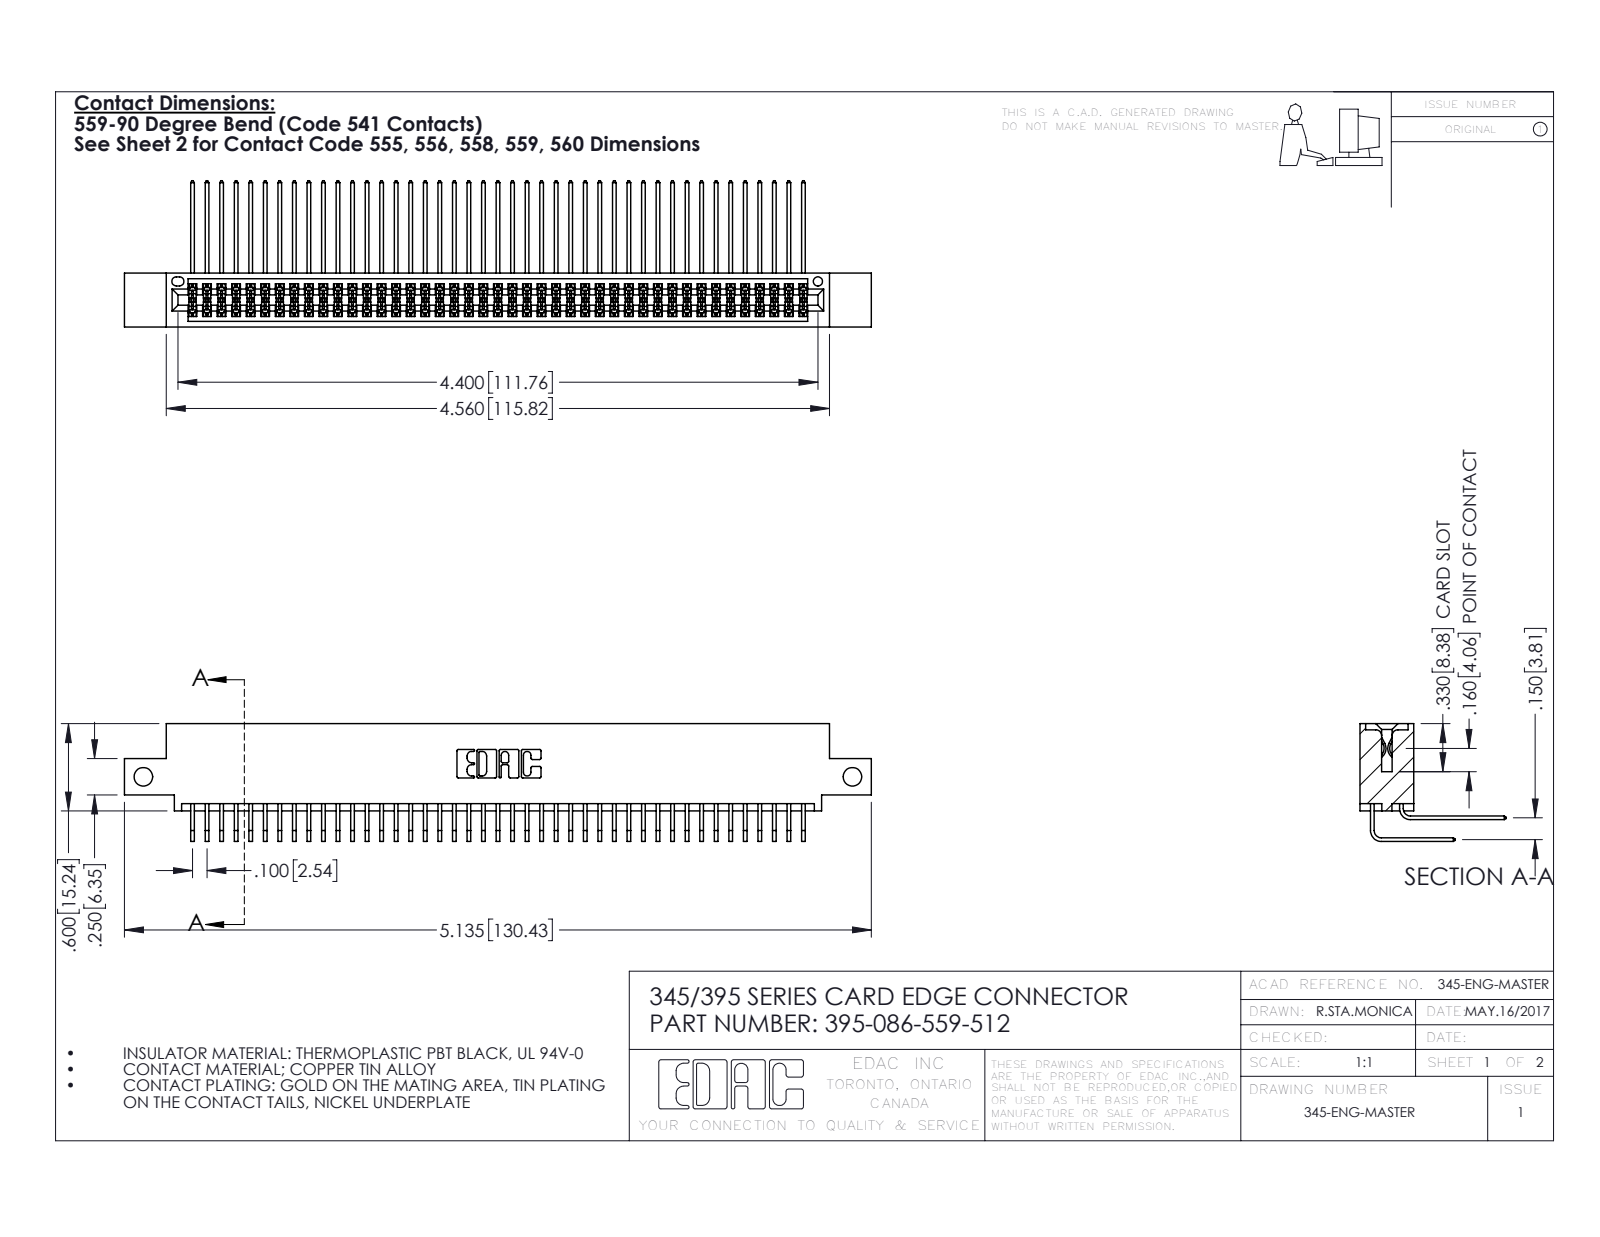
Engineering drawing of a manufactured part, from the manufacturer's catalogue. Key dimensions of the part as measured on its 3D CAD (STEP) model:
Part name (STEP PRODUCT): 345-292-001_559 Tail - 2; 345 Part_0.110 Offset - Side Mount; 345-292-001_558 559 Tail - 1; 395-086-559-512
STEP written by: SolidWorks 2016 (CONFIG_CONTROL_DESIGN)
Units: inches
Bodies: 87 solids, 4602 faces (3094 planar, 1508 cylindrical, 0 other)
Overall size (bounding box): 5.135 × 1.005 × 0.809
Volume: 0.794 in³ · Surface area: 33.4 in²
Round holes (diameter × count): ⌀0.128 ×2, ⌀0.064 ×1
Partial cylindrical surfaces — rounded edges, fillets, slot ends (radius × count): R0.006 ×130, R0.01 ×22, R0.007 ×6, R0.031 ×6, R0.026 ×3, R0.014 ×2, R0.019 ×2, R0.022 ×2
Main face-to-face distances: 0.072, 0.298, 0.37, 0.2, 0.098, 0.272, 0.025, 0.225, 0.175, 0.15
Hole centre spacings: 4.875
